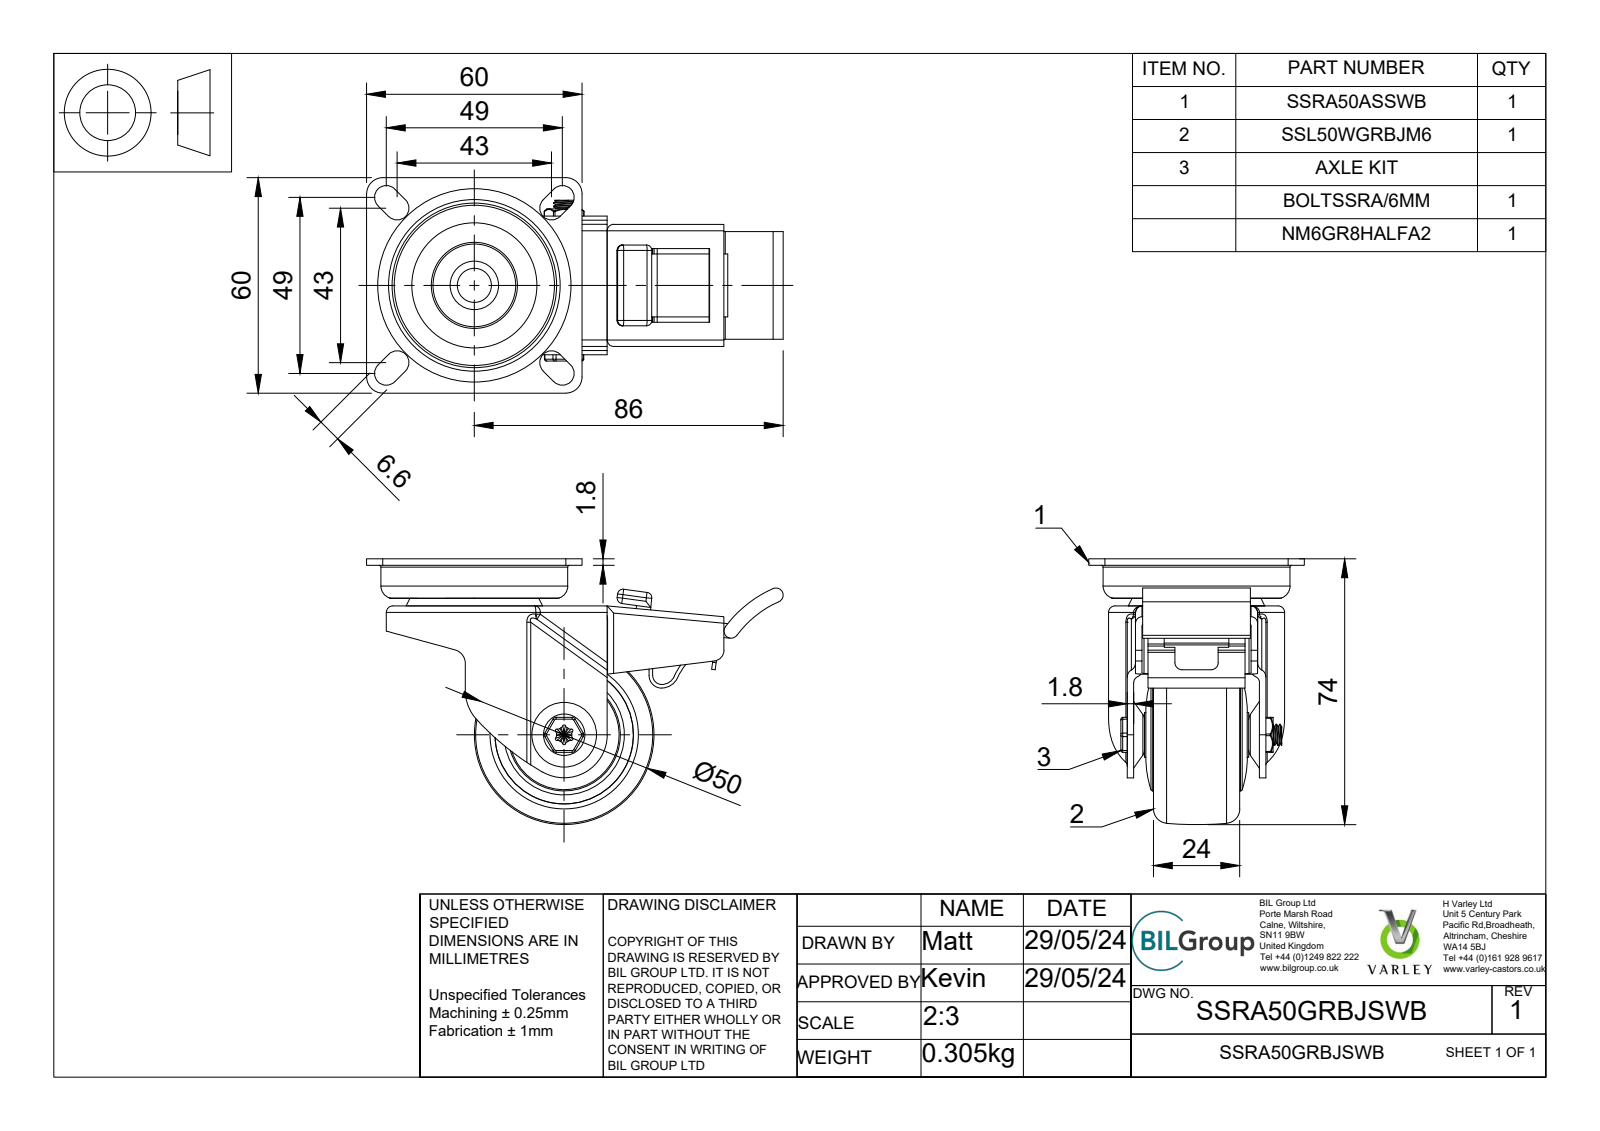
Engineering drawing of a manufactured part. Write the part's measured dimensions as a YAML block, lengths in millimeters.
part_name: "SSRA50GRBJSWB v3; SSRA50ASSWB v1; STAINLESS STEEL TOP PLATE; STAINLESS STEEL FORKS (+8 more)"
step_written_by: "Autodesk Translation Framework v13.14.0.145 (CONFIG_CONTROL_DESIGN)"
units: millimeters
bodies: {solids: 22, faces: 649, planar: 255, cylindrical: 229, other: 165}
overall_size: [116, 74, 60]
volume: 76711
surface_area: 64753
round_holes:
  - {diameter: 6, count: 1}
  - {diameter: 6.1, count: 1}
  - {diameter: 6.2, count: 1}
  - {diameter: 6.8, count: 1}
  - {diameter: 8, count: 1}
  - {diameter: 8.2, count: 1}
  - {diameter: 9.5, count: 1}
  - {diameter: 10.55, count: 1}
  - {diameter: 11.2, count: 1}
  - {diameter: 12.74, count: 1}
  - {diameter: 18.3, count: 1}
  - {diameter: 19.2, count: 1}
round_bosses_or_shafts:
  - {diameter: 52, count: 1}
  - {diameter: 39, count: 1}
  - {diameter: 38, count: 1}
  - {diameter: 31.25, count: 1}
  - {diameter: 26.75, count: 1}
  - {diameter: 18.7, count: 1}
  - {diameter: 18.32, count: 1}
  - {diameter: 15, count: 1}
partial_cylinders:
  - {radius: 1, count: 28}
  - {radius: 1.8, count: 22}
  - {radius: 0.5, count: 12}
  - {radius: 0.9, count: 12}
  - {radius: 1.5, count: 11}
  - {radius: 3.3, count: 8}
  - {radius: 0.4, count: 6}
  - {radius: 2, count: 6}
face_to_face_distances: [1.8, 13.12, 1.81, 30.4, 11.32, 14.92, 7.3, 31.3, 3.19, 14.93]
